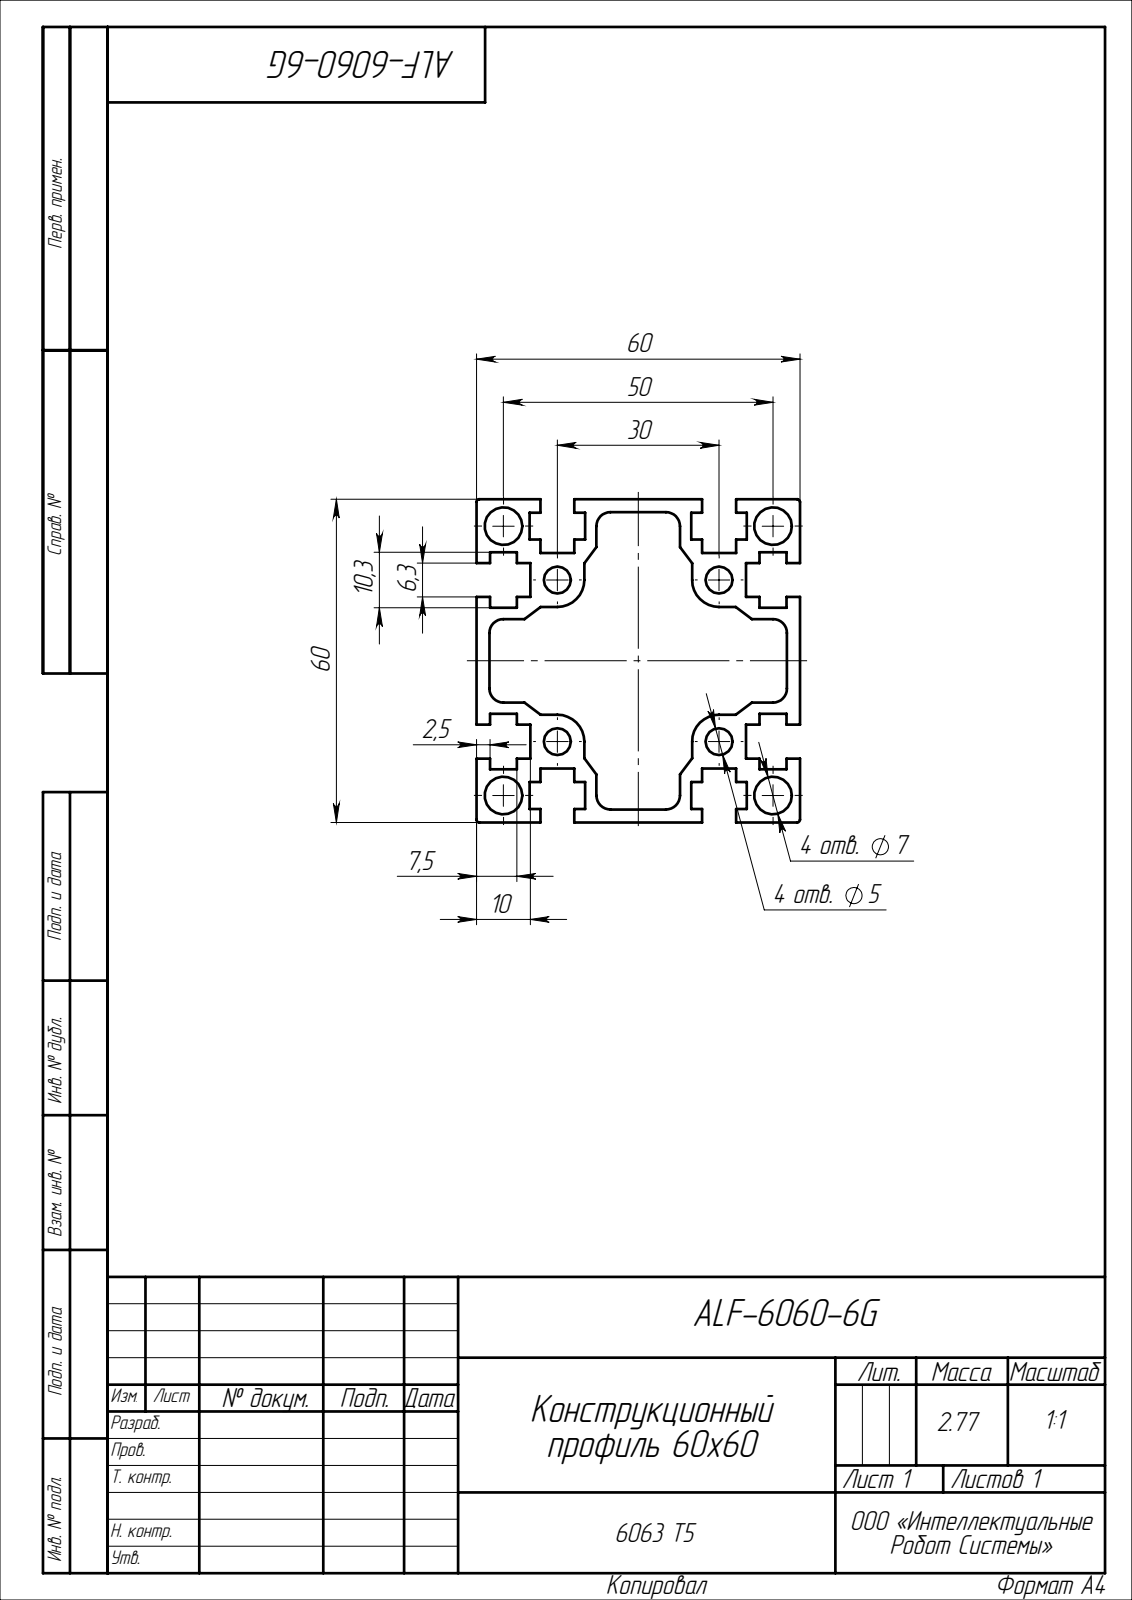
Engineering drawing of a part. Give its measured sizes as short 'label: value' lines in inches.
name: ALF-6060-6G
written by: SolidWorks 2022 (CONFIG_CONTROL_DESIGN)
unit: in
bodies: 1 solid, 162 faces (130 planar, 32 cylindrical, 0 other)
size: 39.37 × 2.362 × 2.362
volume: 62.79 in³; area: 1 251 in²
holes: 4× ⌀0.197, 4× ⌀0.276
rounds: 8× R0.102, 4× R0.02, 4× R0.197
face distances: 2.362, 1.969, 0.079, 0.327, 1.181, 0.098, 0.295, 0.394, 0.094, 2.268
hole spacings: 1.623, 0.557, 1.181, 1.969, 2.227, 1.67, 2.784
